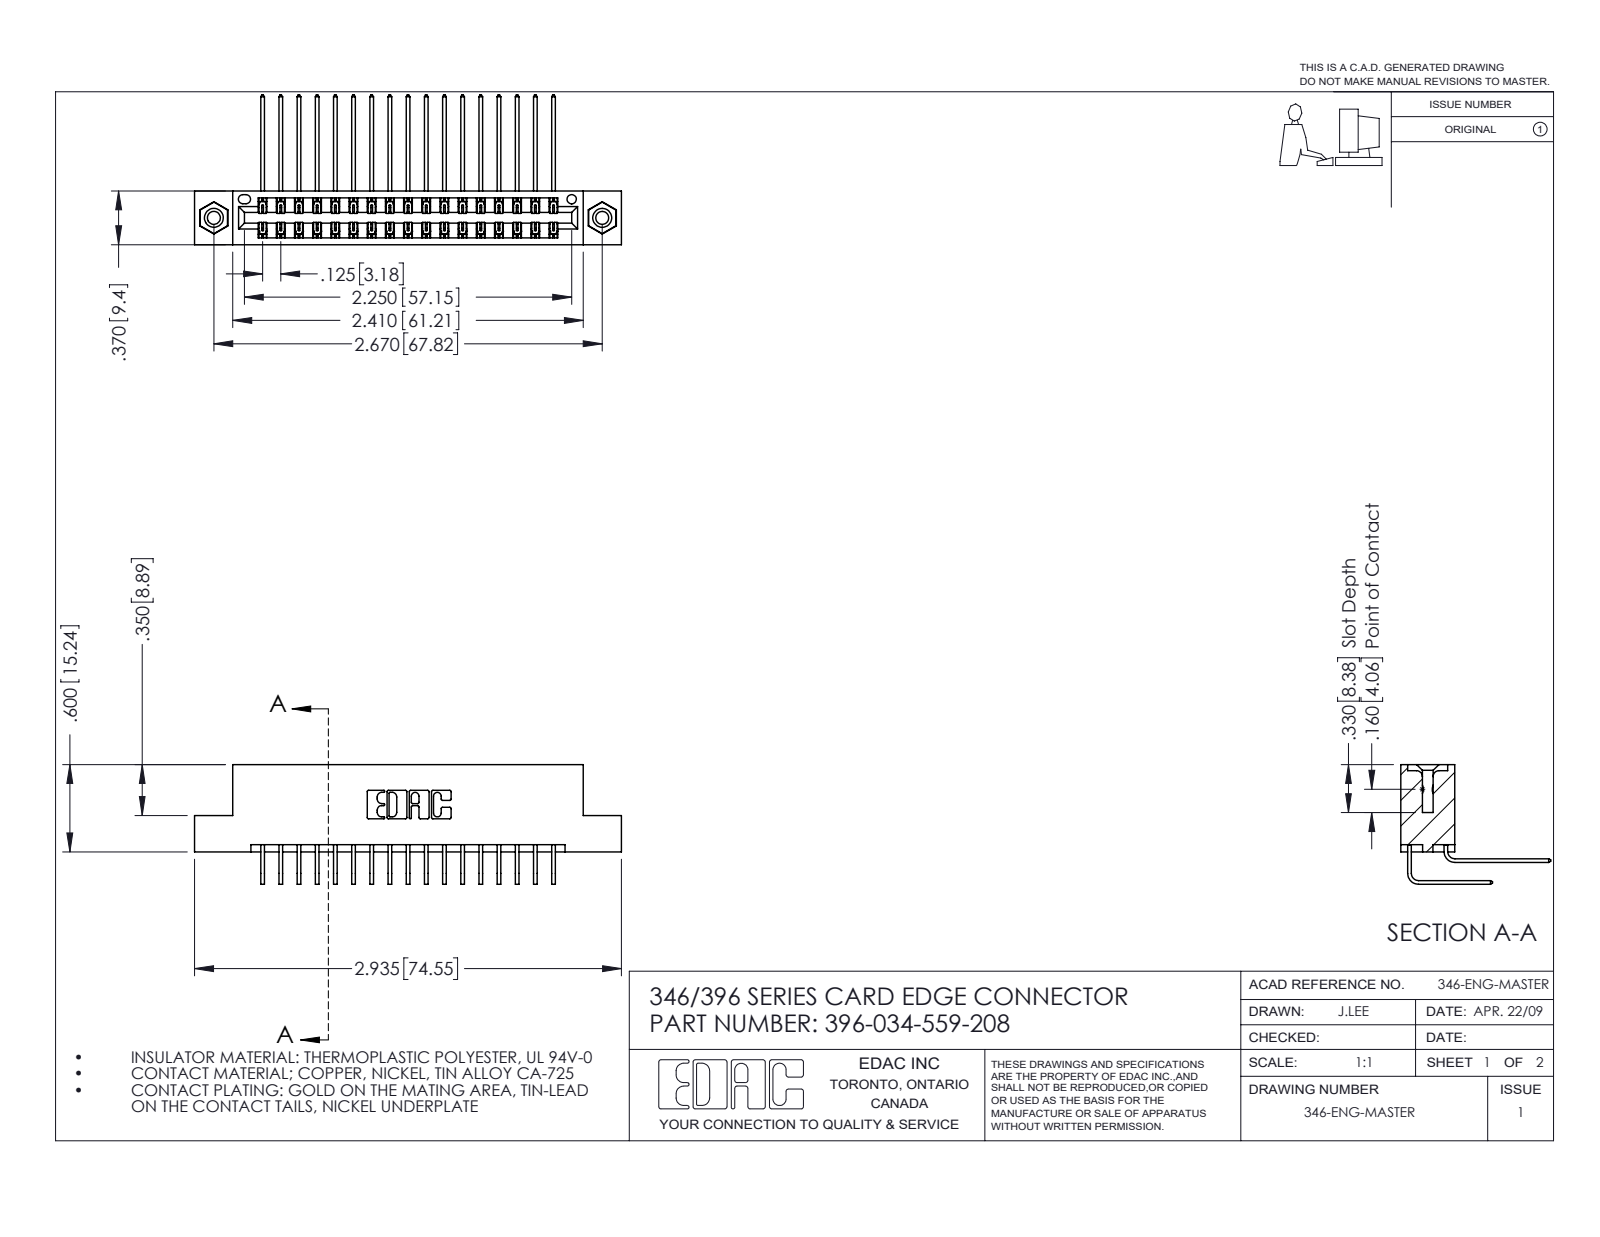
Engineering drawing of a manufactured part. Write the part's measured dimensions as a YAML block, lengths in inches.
part_name: "345-292-001_559 Tail - 2; 346 Part_Flush Mounting Lugs - 0.156 Dia-TI; 396-034-559-208; 345-250-001_345-250-003-102 (+1 more)"
step_written_by: "SolidWorks 2016 (CONFIG_CONTROL_DESIGN)"
units: inches
bodies: {solids: 37, faces: 2018, planar: 1366, cylindrical: 636, other: 16}
overall_size: [2.935, 1.03, 0.823]
volume: 0.443
surface_area: 16.36
round_holes:
  - {diameter: 0.089, count: 2}
  - {diameter: 0.125, count: 2}
  - {diameter: 0.156, count: 2}
  - {diameter: 0.064, count: 1}
round_bosses_or_shafts:
  - {diameter: 0.155, count: 2}
partial_cylinders:
  - {radius: 0.006, count: 51}
  - {radius: 0.01, count: 22}
  - {radius: 0.007, count: 6}
  - {radius: 0.031, count: 6}
  - {radius: 0.026, count: 3}
  - {radius: 0.014, count: 2}
  - {radius: 0.022, count: 2}
  - {radius: 0.024, count: 2}
face_to_face_distances: [0.048, 0.322, 0.25, 0.025, 0.37, 0.072, 0.298, 0.275, 0.148, 0.222]
hole_center_spacings: [0.246, 2.463, 2.67]
